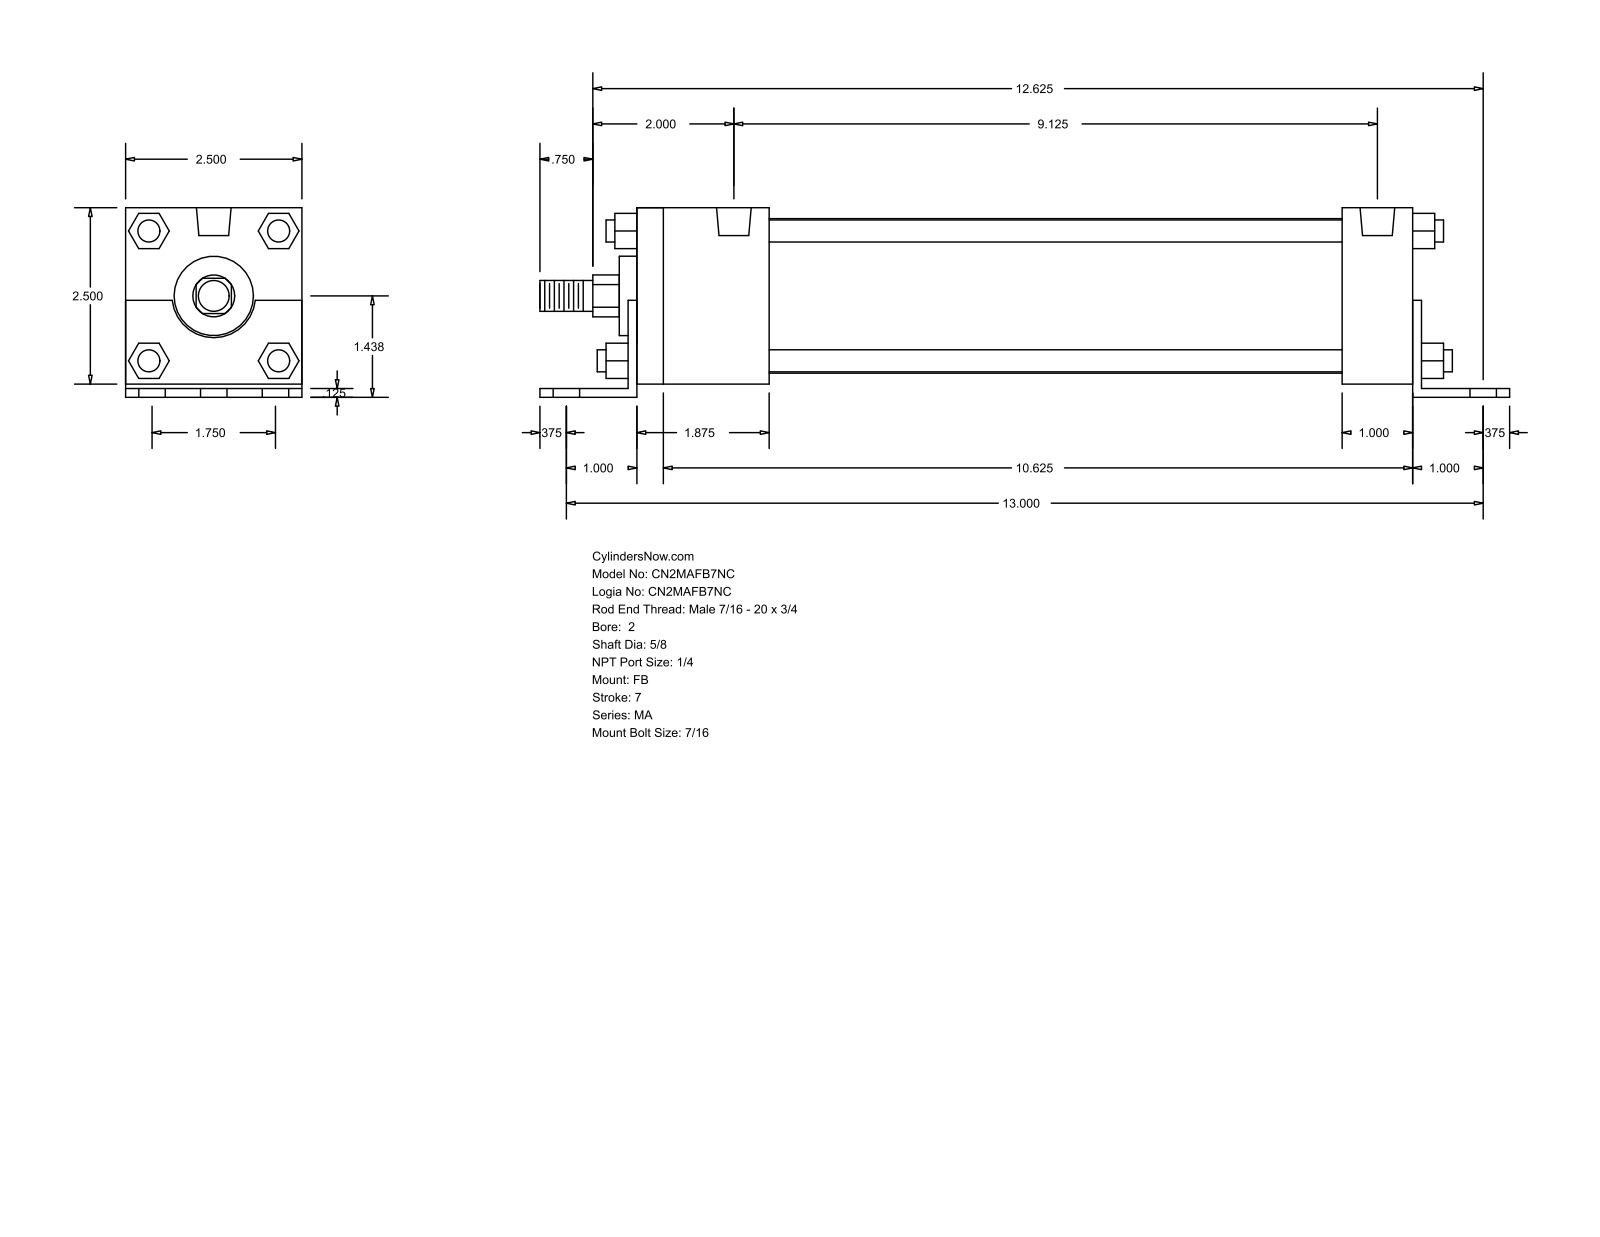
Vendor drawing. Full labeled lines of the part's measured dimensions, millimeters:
Part name (STEP PRODUCT): MA_FB__0200_0.625
STEP written by: GSSL Pune (CONFIG_CONTROL_DESIGN)
Units: millimetres
Bodies: 0 solids, 140 faces (105 planar, 35 cylindrical, 0 other)
Overall size (bounding box): 349.25 × 68.26 × 63.5
Round holes (diameter × count): ⌀11.11 ×6, ⌀7.94 ×4, ⌀12.49 ×2
Round bosses / shafts (diameter × count): ⌀7.94 ×4, ⌀55.63 ×1, ⌀28.57 ×1, ⌀15.88 ×1, ⌀11.11 ×1
Partial cylindrical surfaces — rounded edges, fillets, slot ends (radius × count): R7.54 ×1, R15.05 ×1
Main face-to-face distances: 63.5, 4.76, 3.17, 68.26, 1.59, 3.18, 65.09, 282.57, 279.39, 12.7
Hole centre spacings: 22.23, 330.96, 330.21, 44.12, 44.46, 64.3, 231.77, 270.79
